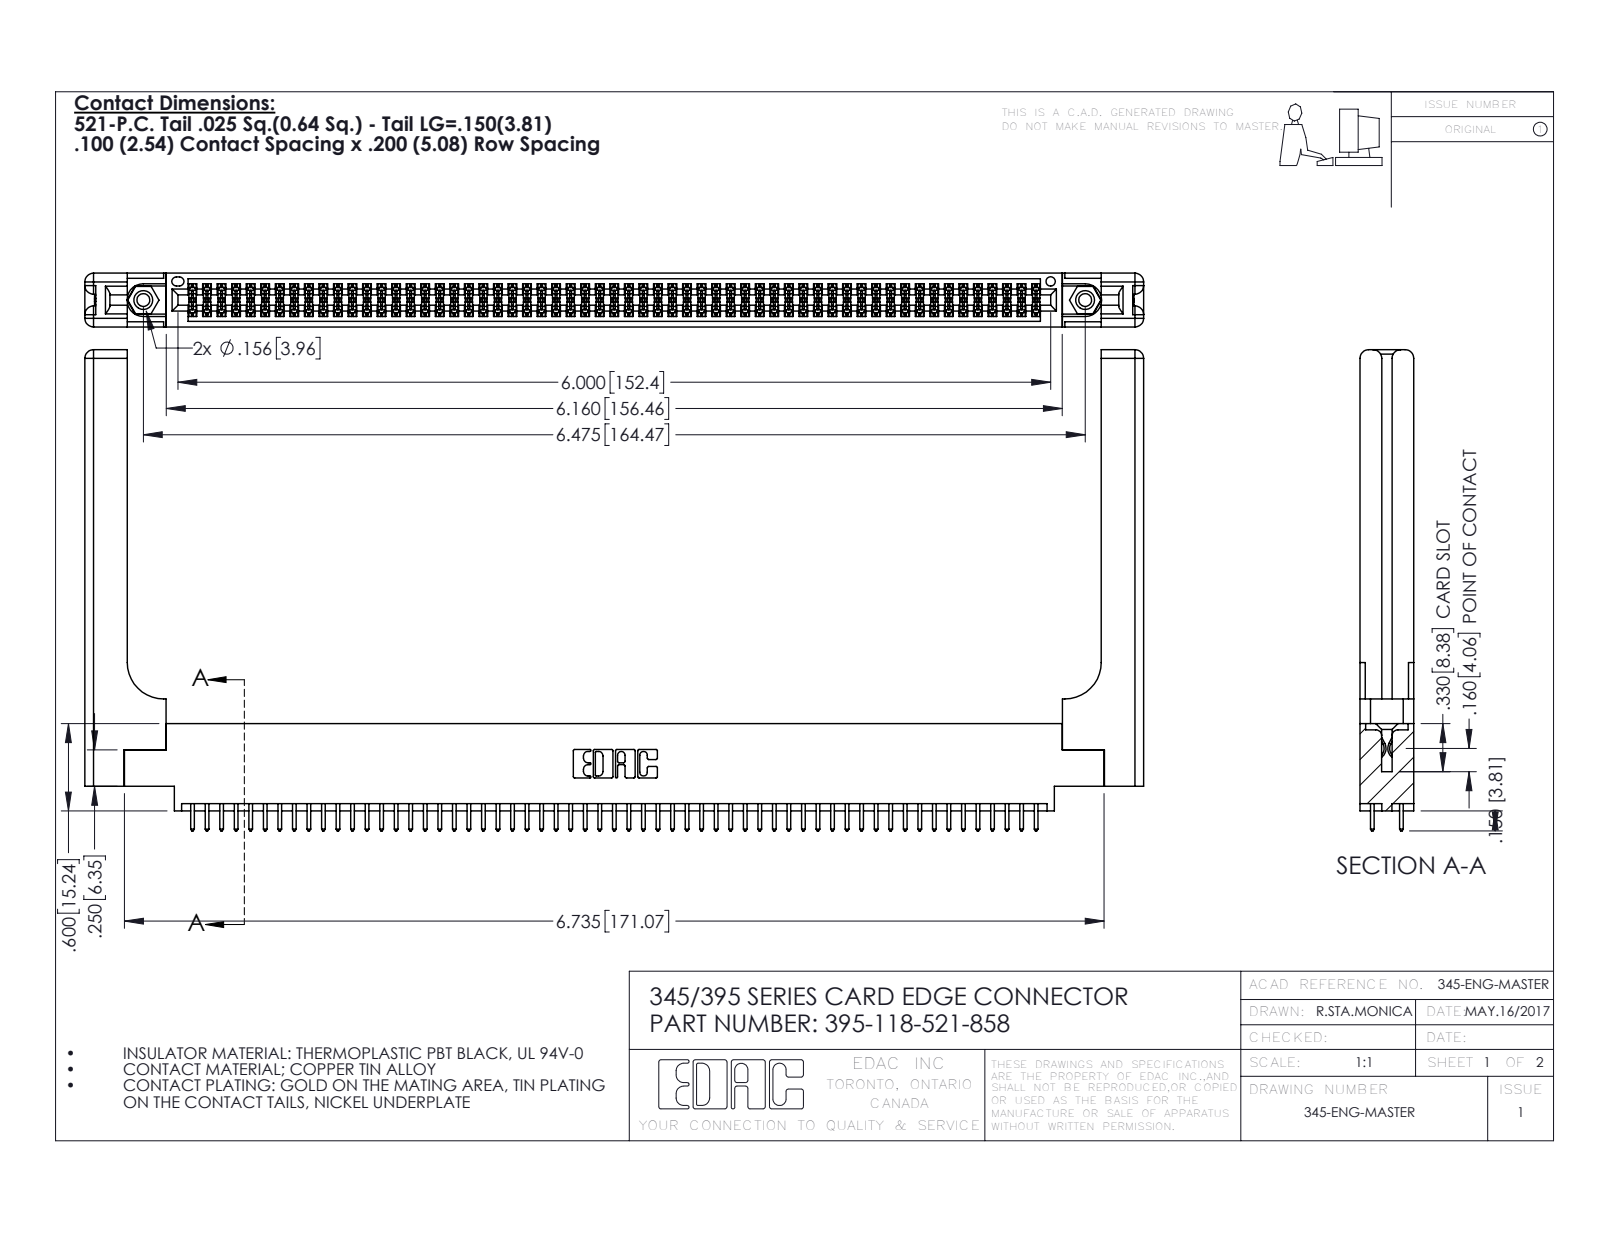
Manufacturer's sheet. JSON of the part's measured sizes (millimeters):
{"part_name": "345 Part_0.170 Offset - 0.156 Dia-TH; 345-220-058_345-220-058; 345-250-001_345-250-001-102; 395-118-521-858 (+1 more)", "step_written_by": "SolidWorks 2016 (CONFIG_CONTROL_DESIGN)", "units": "millimeters", "bodies": {"solids": 123, "faces": 6286, "planar": 4126, "cylindrical": 2100, "other": 60}, "overall_size": [184.9, 84, 9.4], "volume_mm3": 26430, "surface_area_mm2": 31760, "round_holes": [[2.3, 2], [3.2, 2], [4, 2], [1.6, 1]], "round_bosses_or_shafts": [[3.9, 2]], "partial_cylinders_radius": [[0.2, 177], [0.3, 118], [0.3, 22], [1.5, 16], [0.2, 6], [0.8, 6], [0.7, 3], [0.4, 2]], "face_to_face_distances": [1.8, 7.6, 9.4, 2.5, 6.9, 0.6, 5.1, 5.7, 4.4, 3.8], "hole_center_spacings": [6.9, 158.5, 164.5]}
